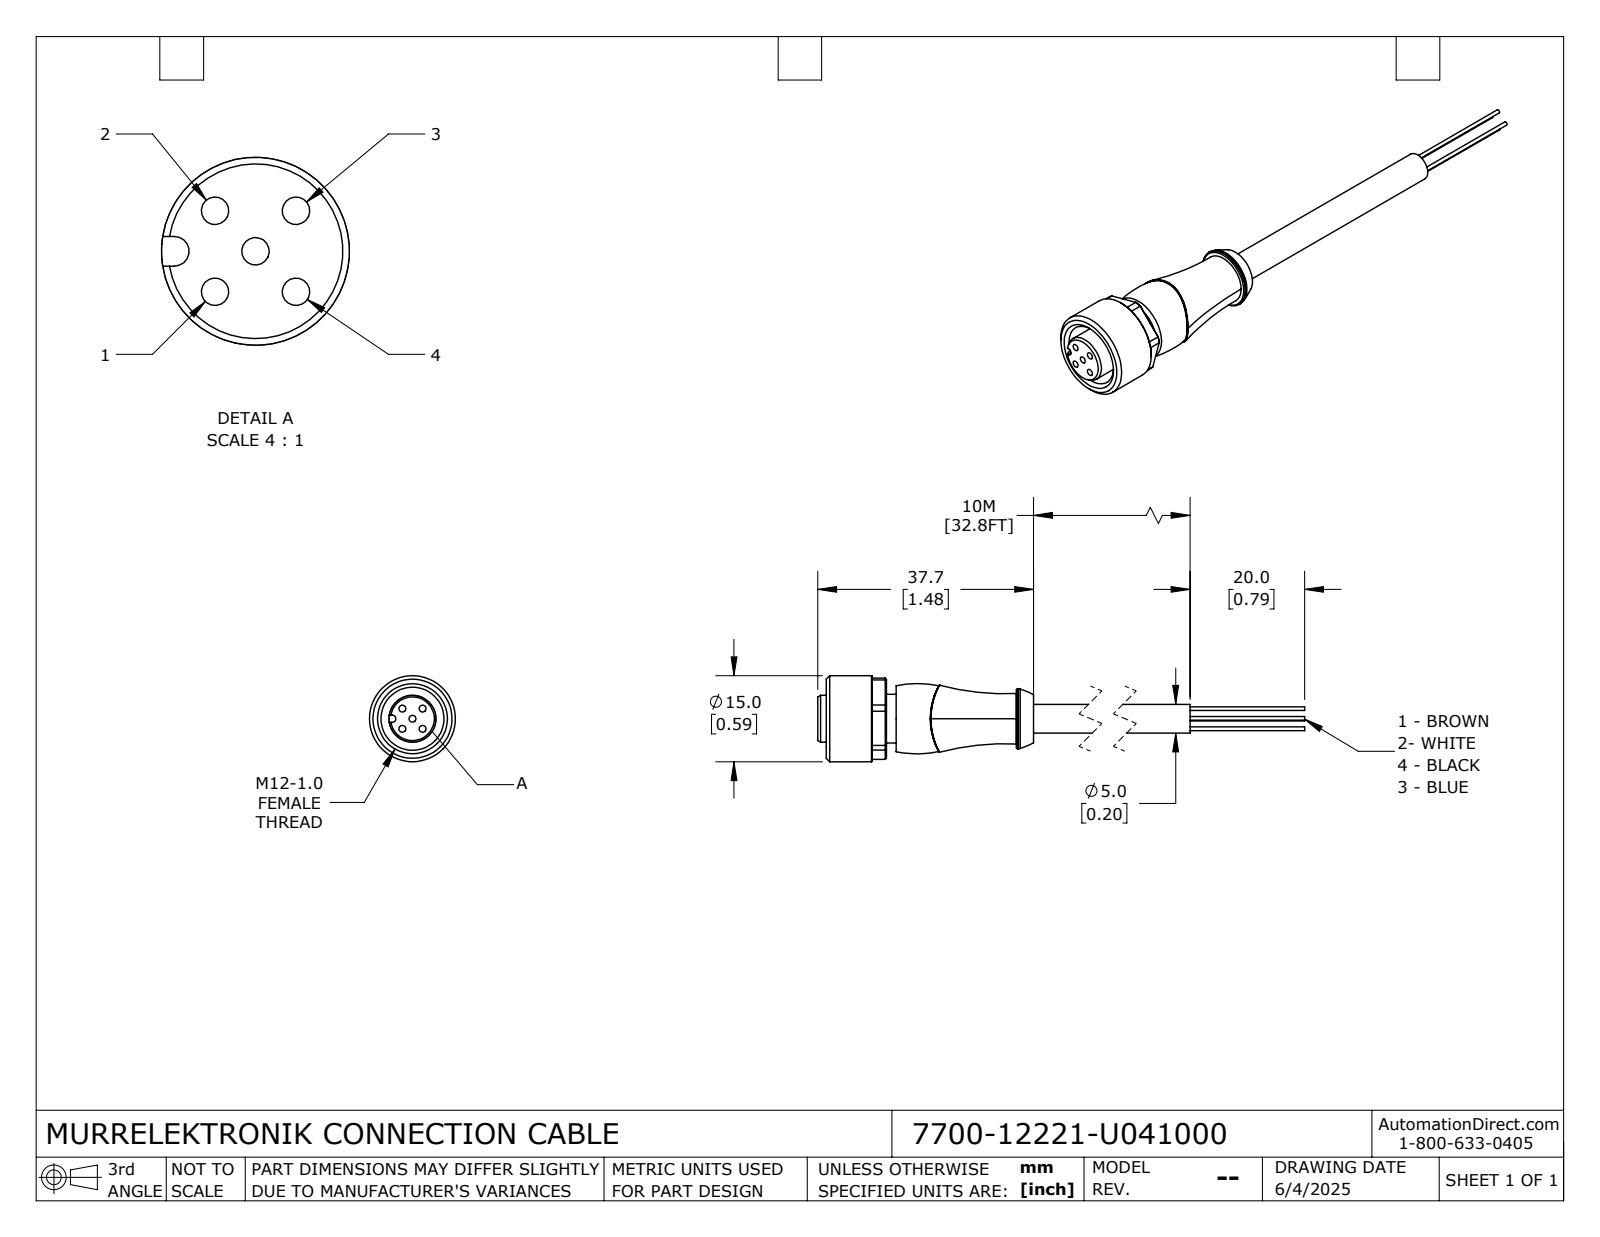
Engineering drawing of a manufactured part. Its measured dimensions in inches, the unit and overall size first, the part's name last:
Units: inches
Overall size (bounding box): 4.043 × 0.591 × 0.591
Round holes (diameter × count): ⌀0.047 ×5, ⌀0.433 ×1
Round bosses / shafts (diameter × count): ⌀0.025 ×4, ⌀0.591 ×1, ⌀0.413 ×1, ⌀0.335 ×1, ⌀0.323 ×1, ⌀0.197 ×1
Partial cylindrical surfaces — rounded edges, fillets, slot ends (radius × count): R0.026 ×1, R0.283 ×1
Main face-to-face distances: 0.118, 1.012, 0.067, 0.512, 0.185, 0.354, 0.472, 0.539, 1.484, 1.13
Hole centre spacings: 0.098, 0.139, 0.139, 0.197
Volume: 0.279 in³ · Surface area: 5.011 in²
Bodies: 1 solid, 110 faces (36 planar, 39 cylindrical, 35 other)
Part name (STEP PRODUCT): 7700-12221-U041000
STEP written by: SolidWorks 2024 (CONFIG_CONTROL_DESIGN)
